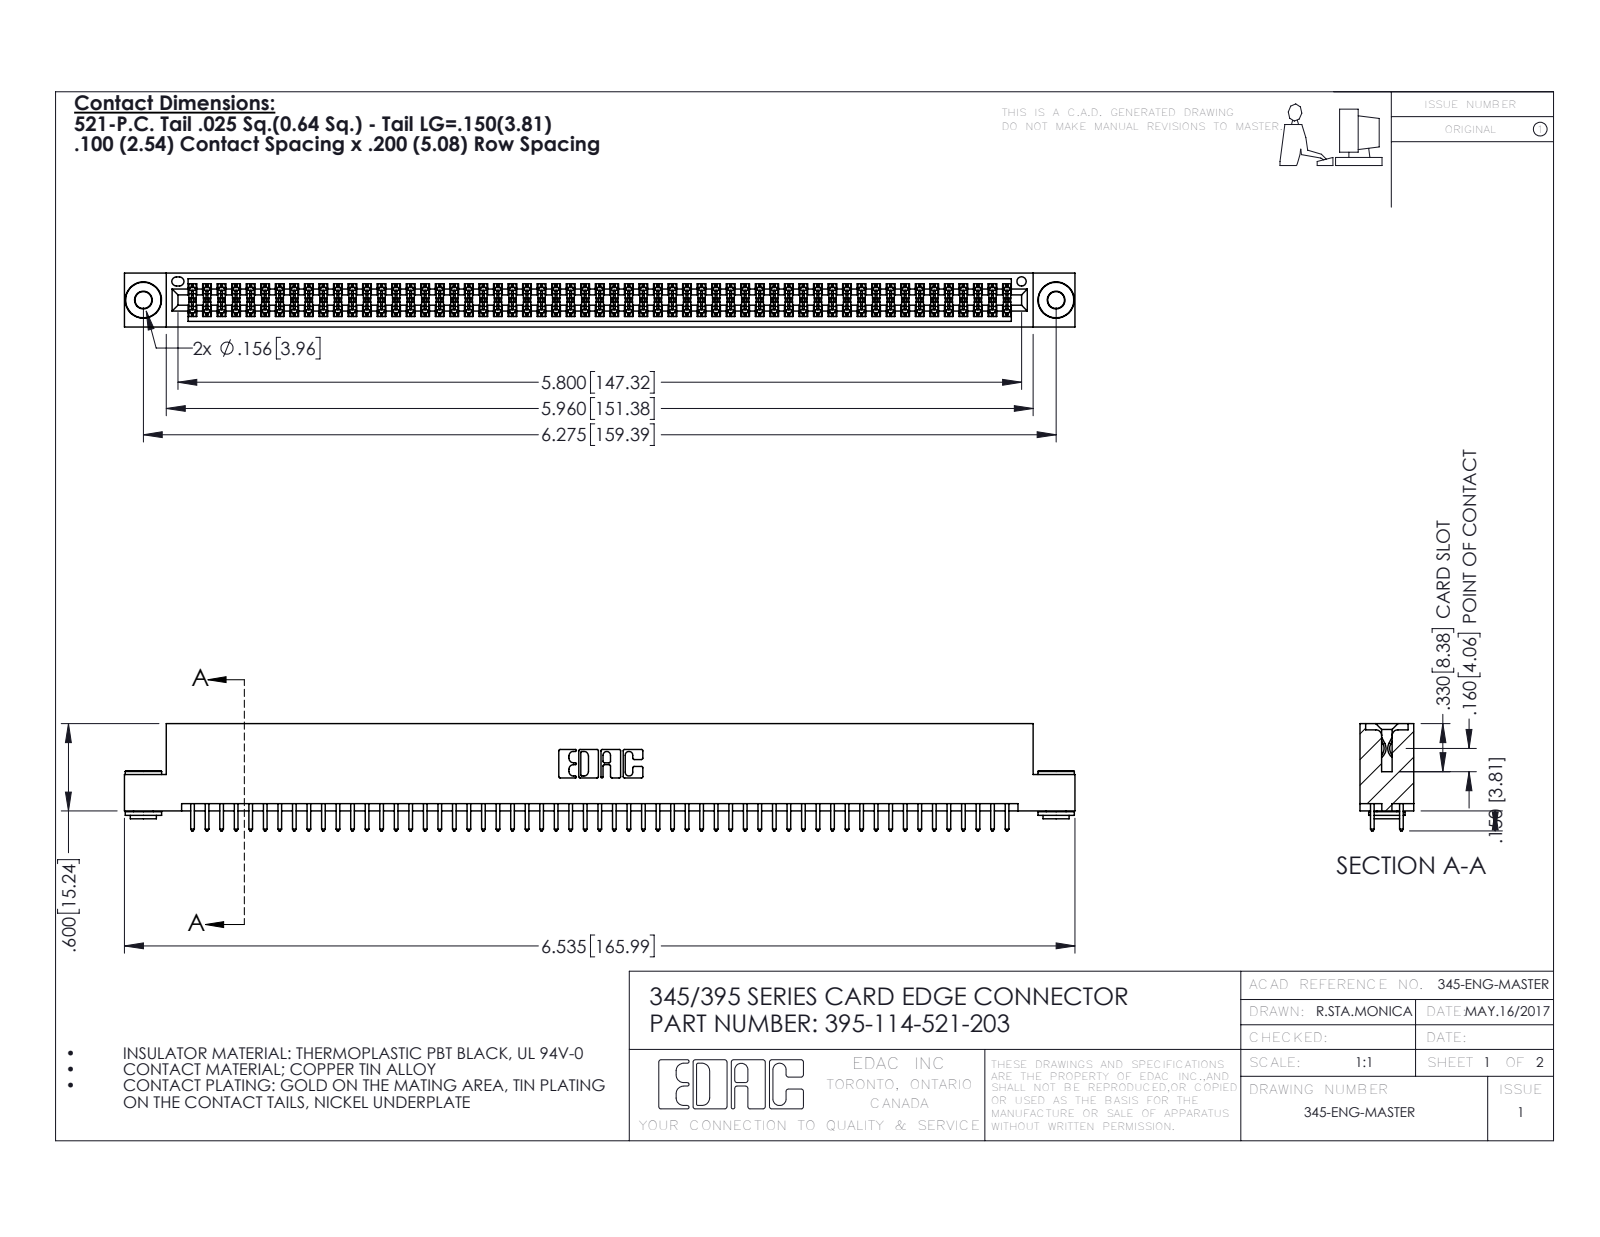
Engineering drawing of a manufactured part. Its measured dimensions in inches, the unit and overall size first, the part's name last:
Units: inches
Overall size (bounding box): 6.535 × 0.737 × 0.37
Round holes (diameter × count): ⌀0.116 ×2, ⌀0.156 ×2, ⌀0.064 ×1
Round bosses / shafts (diameter × count): ⌀0.25 ×2, ⌀0.18 ×2, ⌀0.136 ×2
Partial cylindrical surfaces — rounded edges, fillets, slot ends (radius × count): R0.006 ×171, R0.01 ×114, R0.01 ×22, R0.007 ×6, R0.031 ×6, R0.026 ×3, R0.014 ×2, R0.019 ×2
Main face-to-face distances: 0.072, 0.298, 0.2, 0.025, 0.098, 0.272, 0.37, 0.225, 0.175, 0.149
Hole centre spacings: 0.27, 6.039, 6.275
Volume: 0.991 in³ · Surface area: 37.5 in²
Bodies: 117 solids, 5864 faces (3852 planar, 2004 cylindrical, 8 other)
Part name (STEP PRODUCT): 345-292-001_345-293-121; 345 Part_Flush Mounting Lugs - 0.156 Dia-TH; 395-114-521-203; 345-250-002_345-250-002-102
STEP written by: SolidWorks 2016 (CONFIG_CONTROL_DESIGN)
